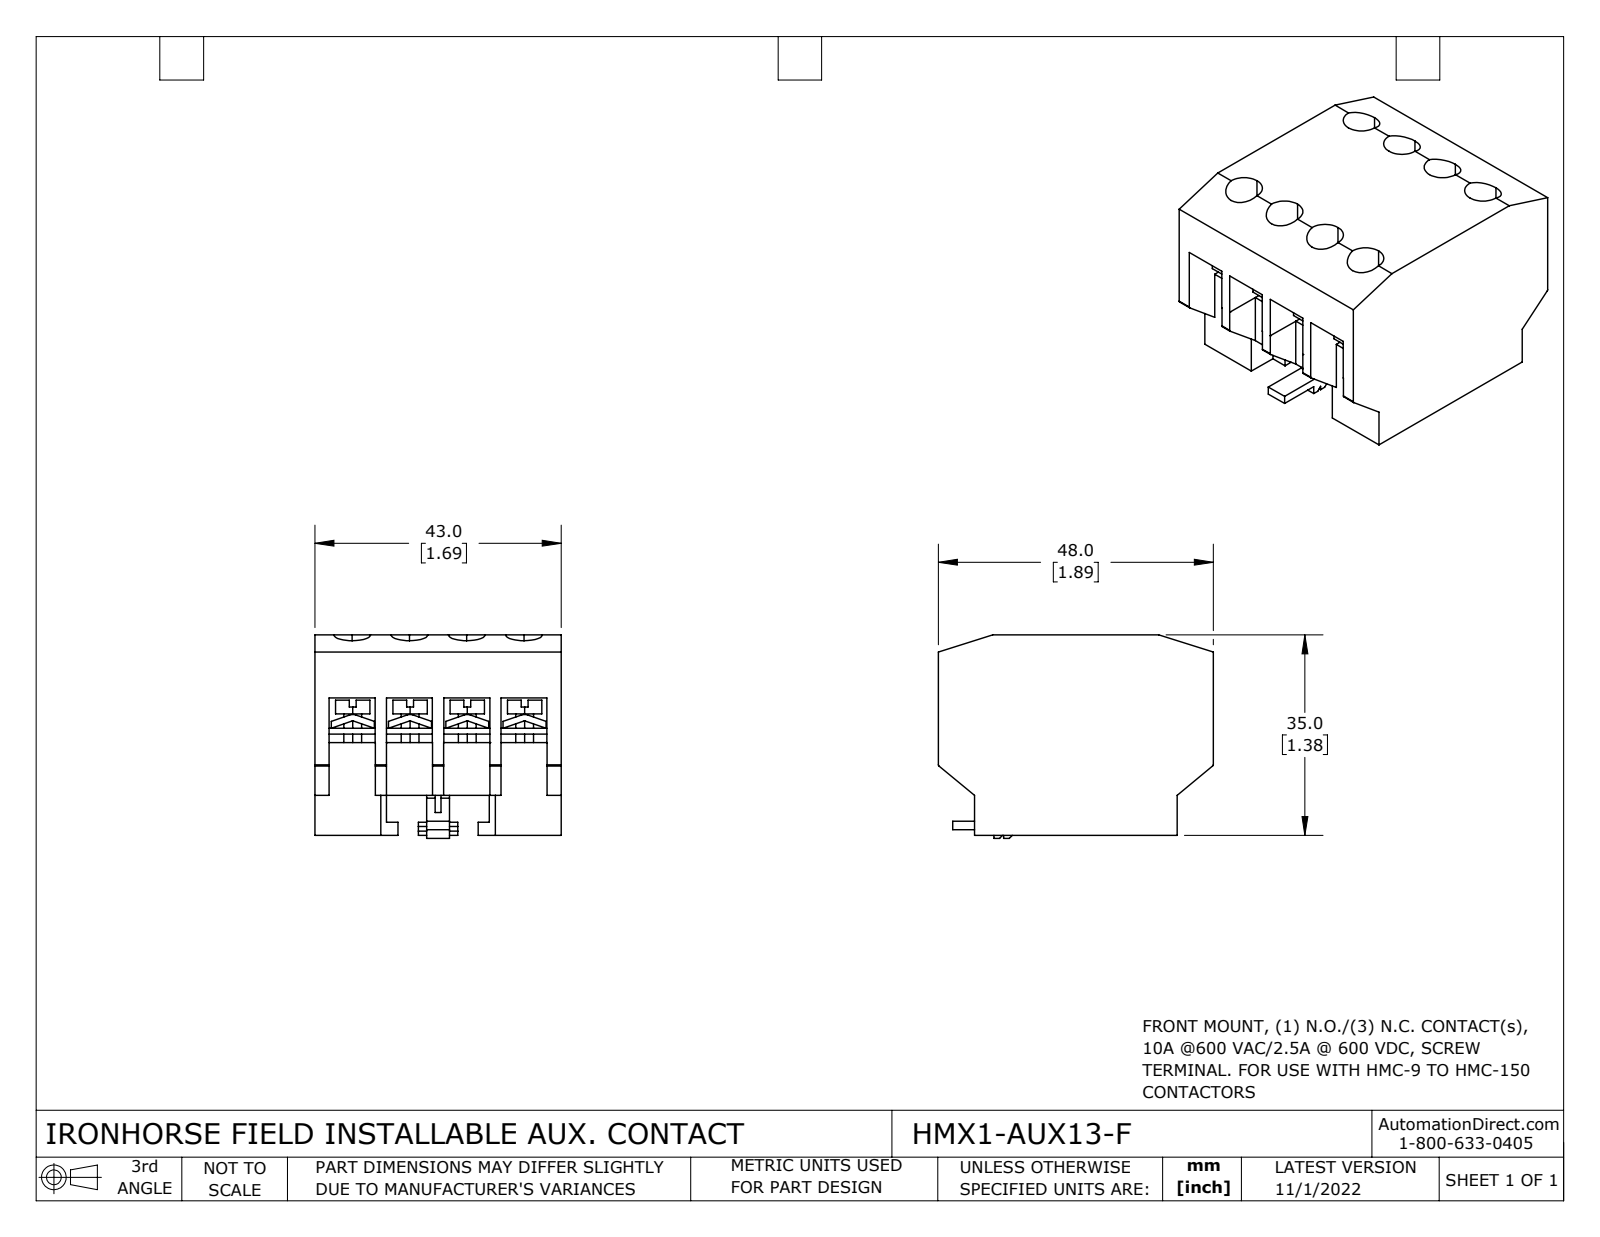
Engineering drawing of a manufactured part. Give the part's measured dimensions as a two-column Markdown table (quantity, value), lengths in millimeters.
| quantity | value |
| --- | --- |
| part name | HMX1-AUX13-F |
| STEP written by | SolidWorks 2021 (CONFIG_CONTROL_DESIGN) |
| units | millimeters |
| bodies | 9 solids, 536 faces (426 planar, 110 cylindrical, 0 other) |
| overall size | 48 × 43 × 35.5 |
| volume | 46 880 mm³ |
| surface area | 20 730 mm² |
| round holes (diameter × count) | 6.4 × 8 |
| round bosses / shafts (diameter × count) | 6 × 8, 3.1 × 8 |
| partial cylindrical surfaces (radius × count) | 0.3 × 6, 1.5 × 4, 0.5 × 2, 2.5 × 1, 4 × 1 |
| main face-to-face distances | 1.5, 43, 6.3, 7.8, 10, 8, 41.7, 11, 2.5, 20 |
| hole center spacings | 10, 30.7, 20, 29, 35.2, 30, 41.7 |
